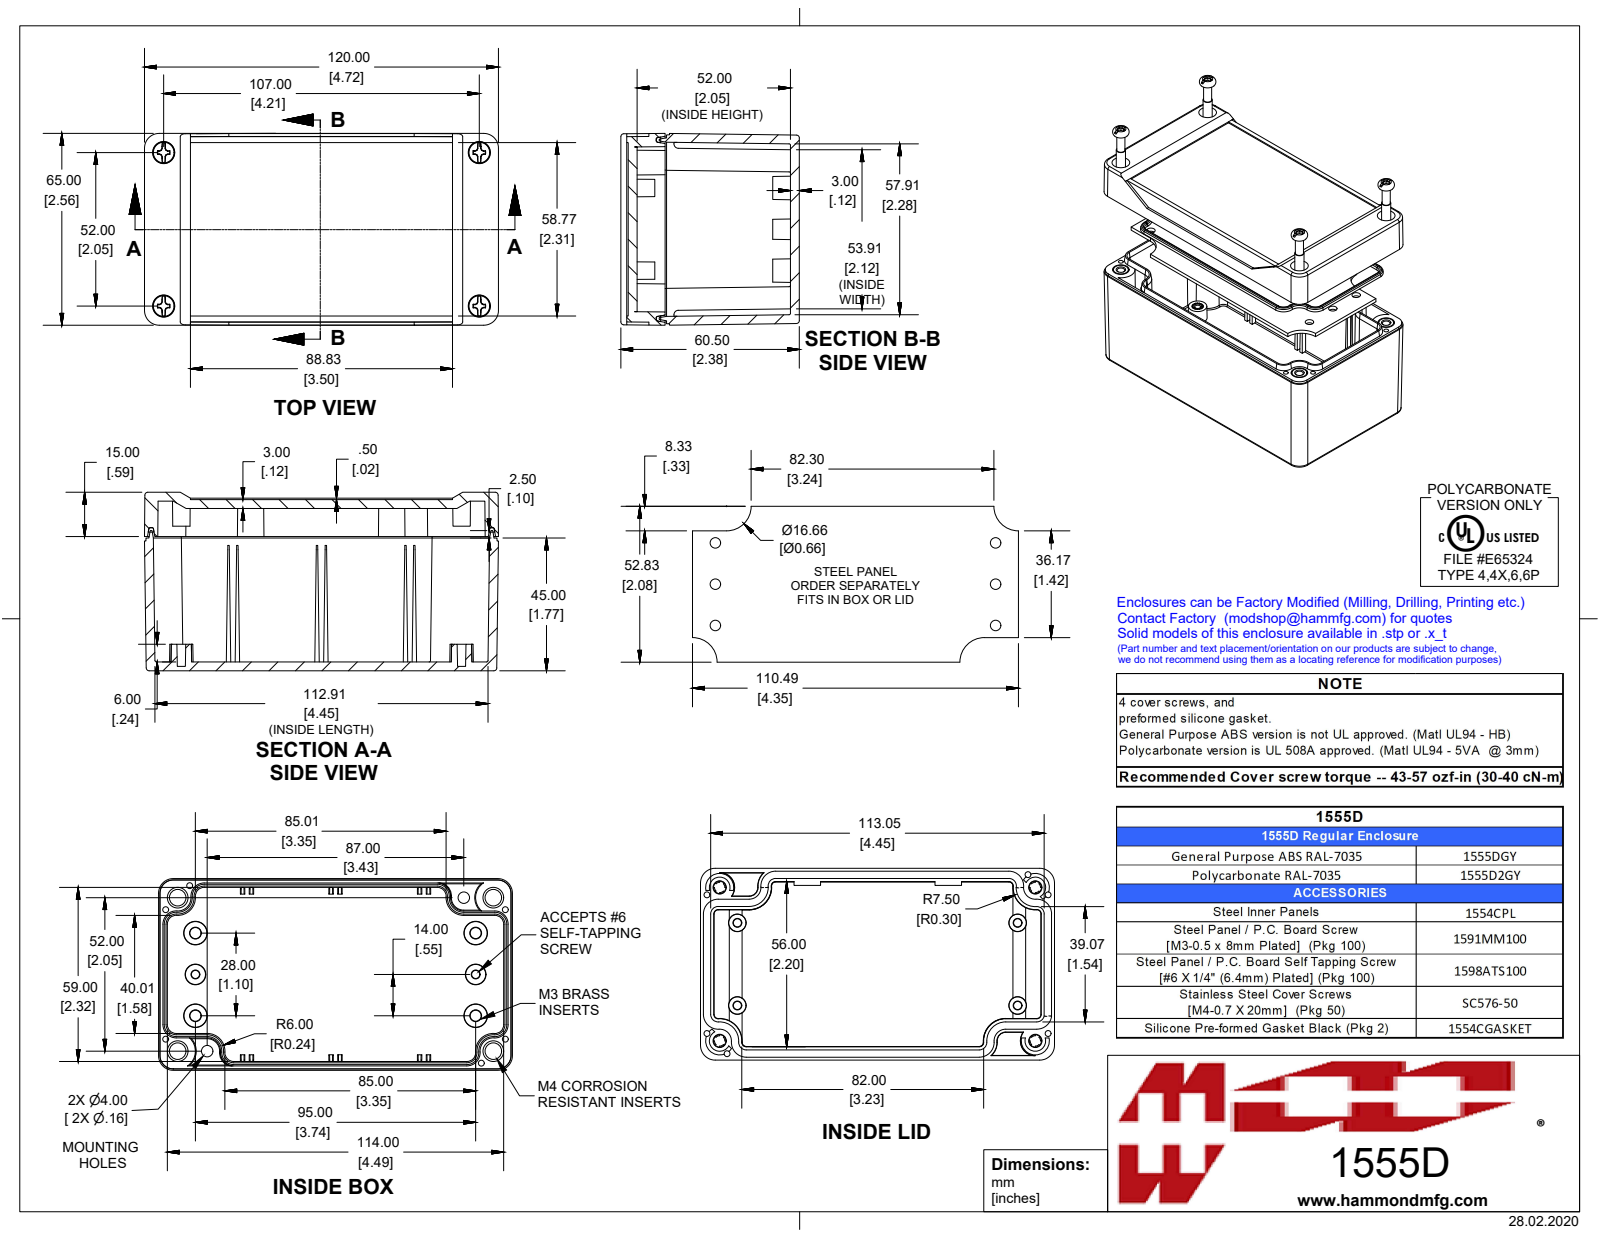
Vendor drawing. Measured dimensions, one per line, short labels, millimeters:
name: 1555D2GY
written by: SolidWorks 2019 (AUTOMOTIVE_DESIGN)
unit: mm
bodies: 15 solids, 1406 faces (440 planar, 358 cylindrical, 608 other)
size: 120 × 65 × 60.5
volume: 120 600 mm³; area: 90 640 mm²
holes: 12× ⌀2, 4× ⌀2.5, 4× ⌀3.3, 4× ⌀7
bosses: 4× ⌀6.4, 4× ⌀5.5, 4× ⌀5.3, 4× ⌀4.8, 4× ⌀3.9, 4× ⌀3.9, 4× ⌀3.8, 4× ⌀3.4
rounds: 24× R0.5, 8× R1, 8× R5, 4× R1.4, 4× R1.8, 4× R2.1, 4× R4.7, 2× R1.5
face distances: 3, 55, 58, 52, 1.5, 9.5, 4.5, 3.5, 12.5, 0.5
hole spacings: 5, 5.7, 10.7, 49.7, 111.4, 119, 121.8, 1.6
